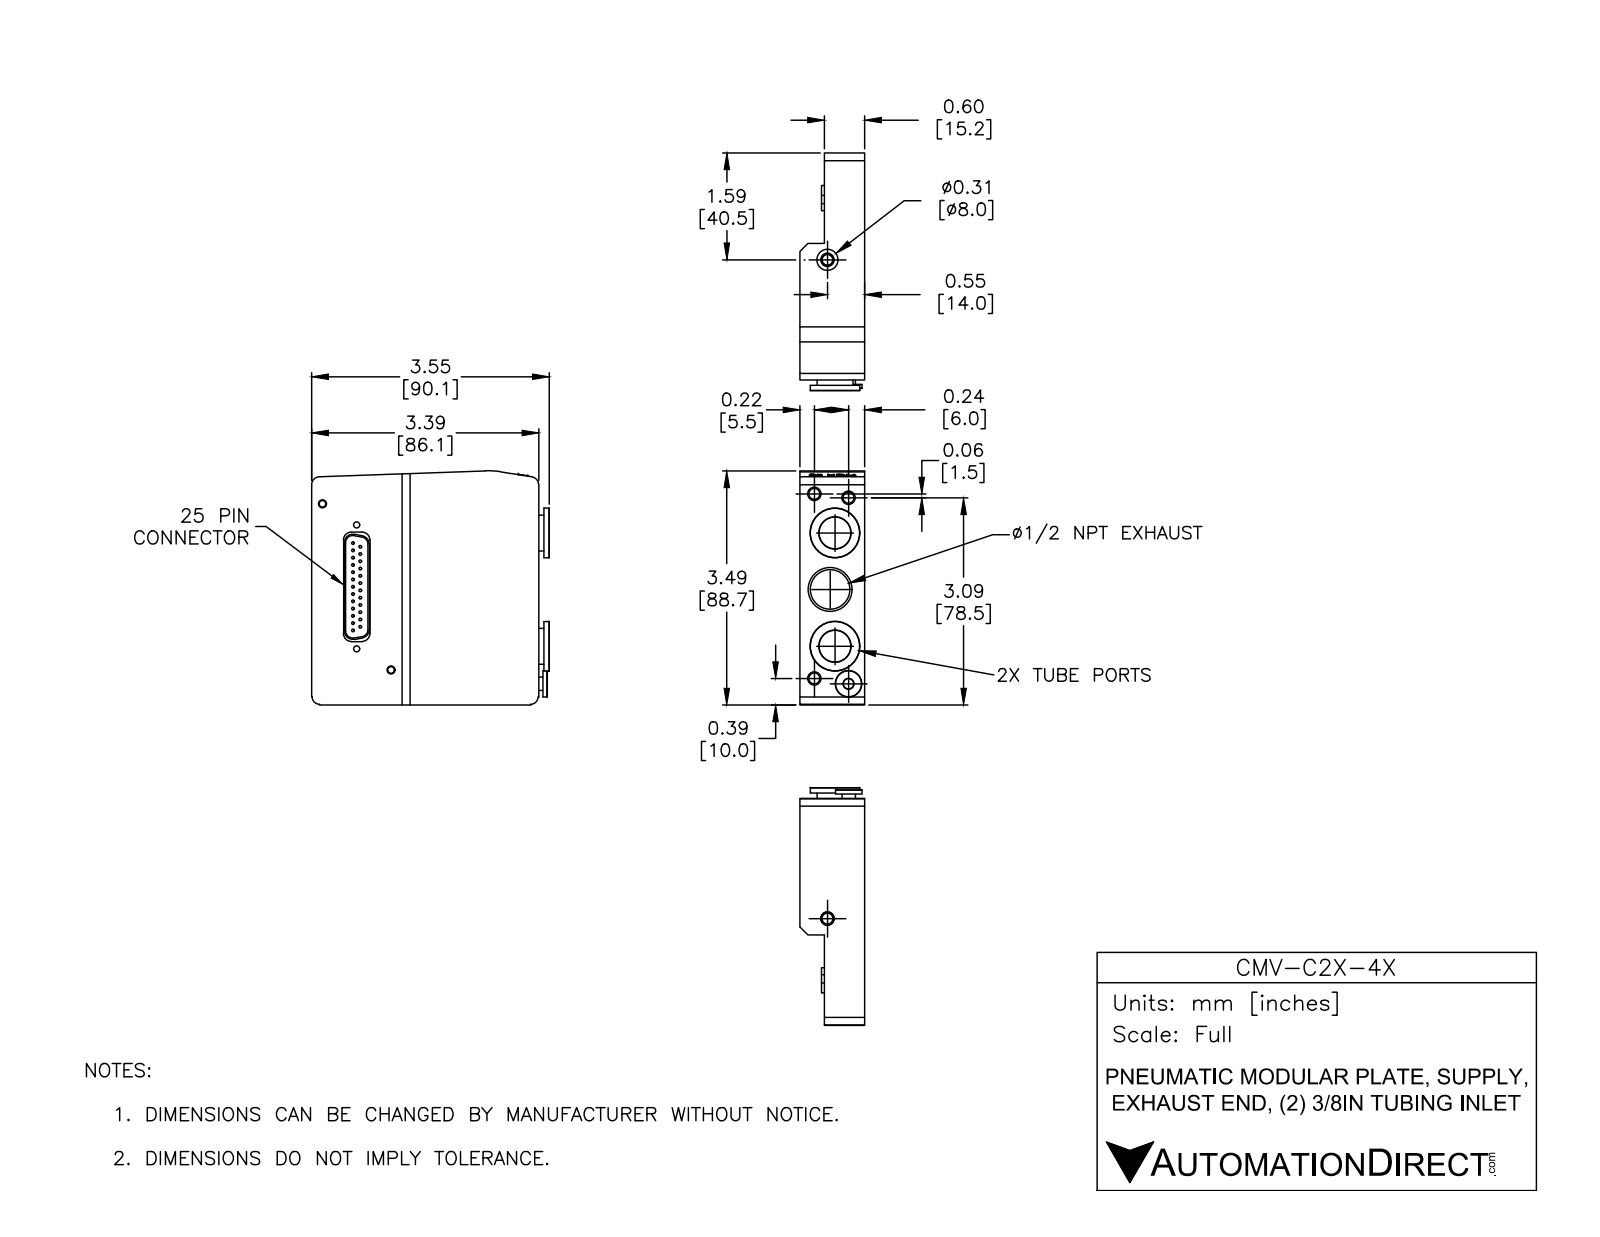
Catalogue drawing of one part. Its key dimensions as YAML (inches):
part_name: "CMV-C2X-4X"
step_written_by: "SolidWorks 2019 (AUTOMOTIVE_DESIGN)"
units: inches
bodies: {solids: 32, faces: 747, planar: 391, cylindrical: 259, other: 97}
overall_size: [3.563, 3.554, 1.26]
volume: 7.686
surface_area: 71.18
round_holes:
  - {diameter: 0.161, count: 3}
  - {diameter: 0.165, count: 3}
  - {diameter: 0.091, count: 2}
  - {diameter: 0.098, count: 2}
  - {diameter: 0.182, count: 2}
  - {diameter: 0.38, count: 2}
  - {diameter: 0.535, count: 2}
  - {diameter: 0.736, count: 2}
  - {diameter: 0.157, count: 1}
  - {diameter: 0.173, count: 1}
  - {diameter: 0.205, count: 1}
  - {diameter: 0.315, count: 1}
round_bosses_or_shafts:
  - {diameter: 0.056, count: 26}
  - {diameter: 0.039, count: 25}
  - {diameter: 0.059, count: 4}
  - {diameter: 0.74, count: 2}
  - {diameter: 0.246, count: 2}
  - {diameter: 0.226, count: 2}
  - {diameter: 0.165, count: 2}
  - {diameter: 0.127, count: 2}
partial_cylinders:
  - {radius: 0.093, count: 12}
  - {radius: 0.118, count: 12}
  - {radius: 0.059, count: 4}
  - {radius: 0.106, count: 4}
  - {radius: 0.127, count: 4}
  - {radius: 0.157, count: 4}
  - {radius: 1.181, count: 1}
face_to_face_distances: [0.965, 0.039, 0.598, 0.366, 0.925, 0.559, 1.004, 0.079, 0.638, 3.39]
hole_center_spacings: [0.531, 0.6, 0.85, 2.756, 2.807, 0.081, 0.139, 0.228]
